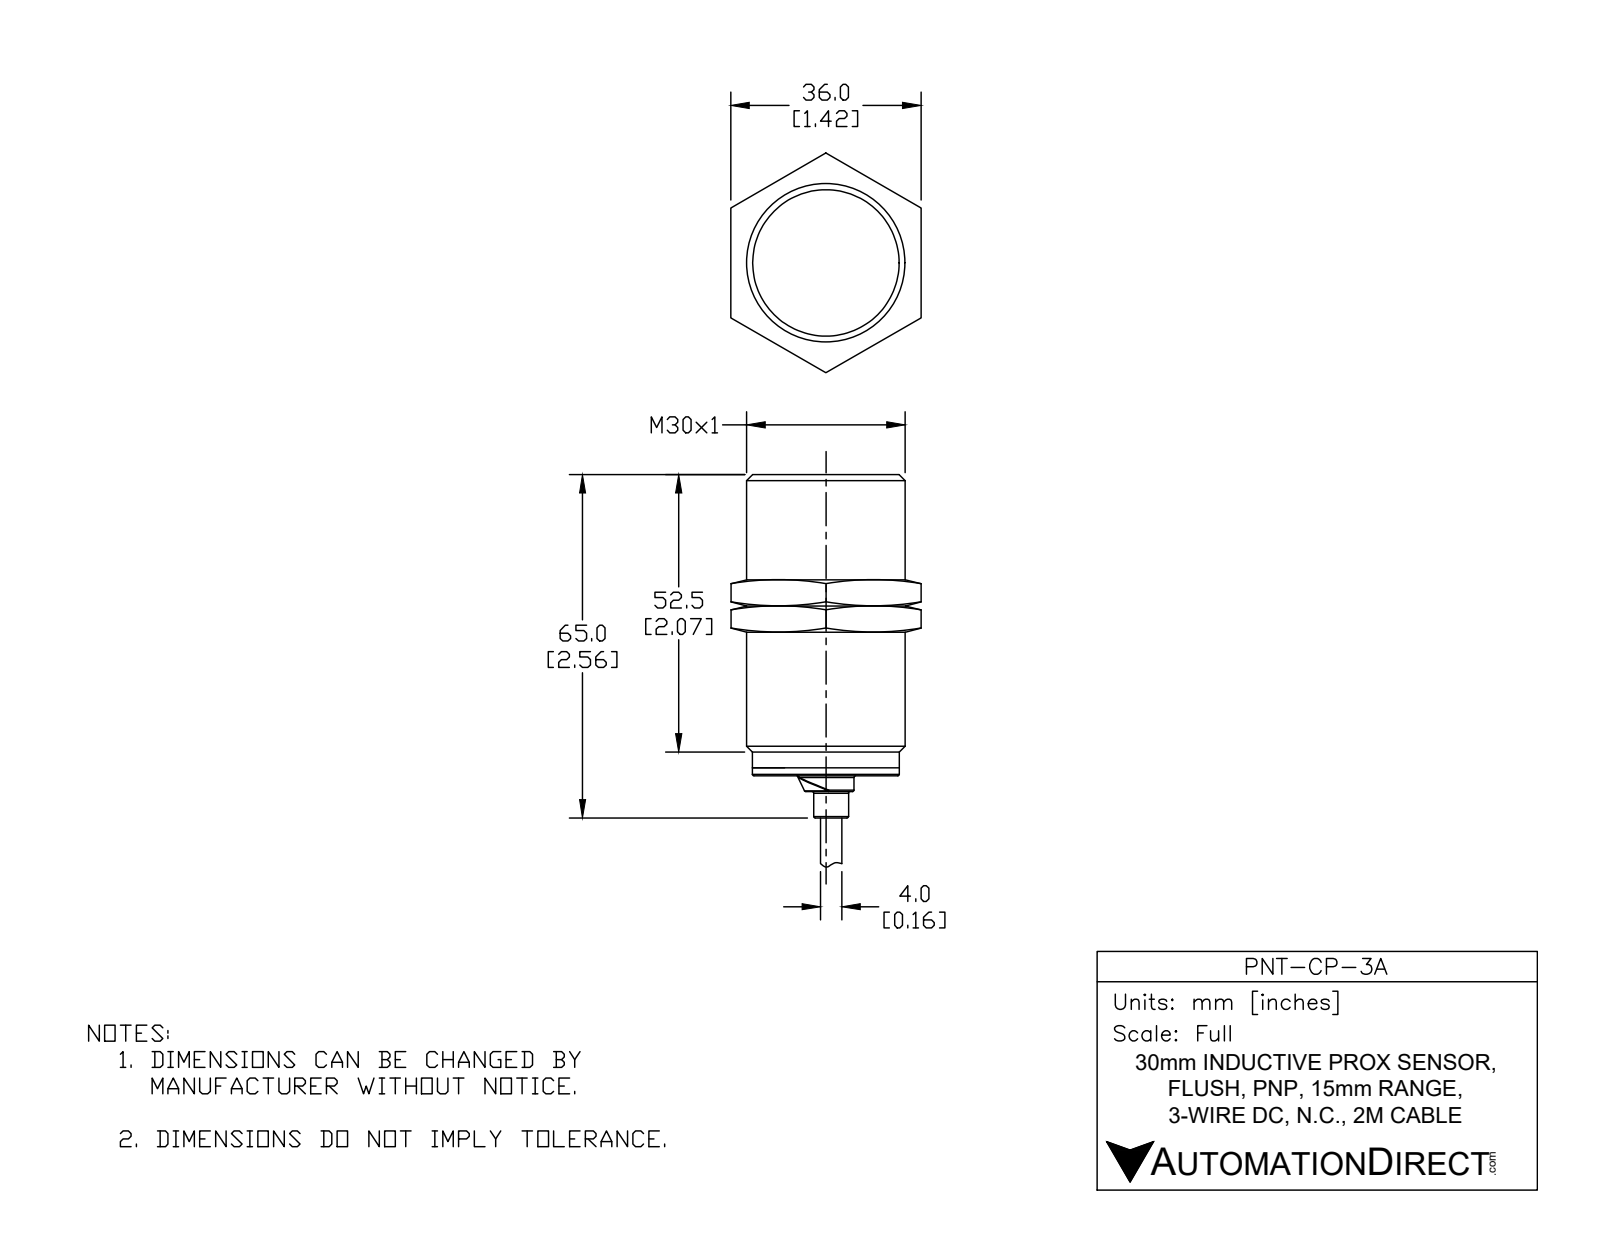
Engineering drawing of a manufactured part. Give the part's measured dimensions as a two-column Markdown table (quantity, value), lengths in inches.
| quantity | value |
| --- | --- |
| part name | PNT-CP-3A |
| STEP written by | SolidWorks 2017 (AUTOMOTIVE_DESIGN) |
| units | inches |
| bodies | 1 solid, 74 faces (14 planar, 30 cylindrical, 30 other) |
| overall size | 4.559 × 1.181 × 1.181 |
| volume | 2.487 in³ |
| surface area | 11.9 in² |
| round holes (diameter × count) | 0.162 × 1 |
| round bosses / shafts (diameter × count) | 0.049 × 6, 1.181 × 1, 1.095 × 1, 1.094 × 1, 0.417 × 1, 0.26 × 1, 0.157 × 1 |
| partial cylindrical surfaces (radius × count) | 0.077 × 1 |
| main face-to-face distances | 2.244, 2.362, 0.118, 2.28, 2.559, 0.315, 0.197, 4.559, 2.315, 2.197 |
